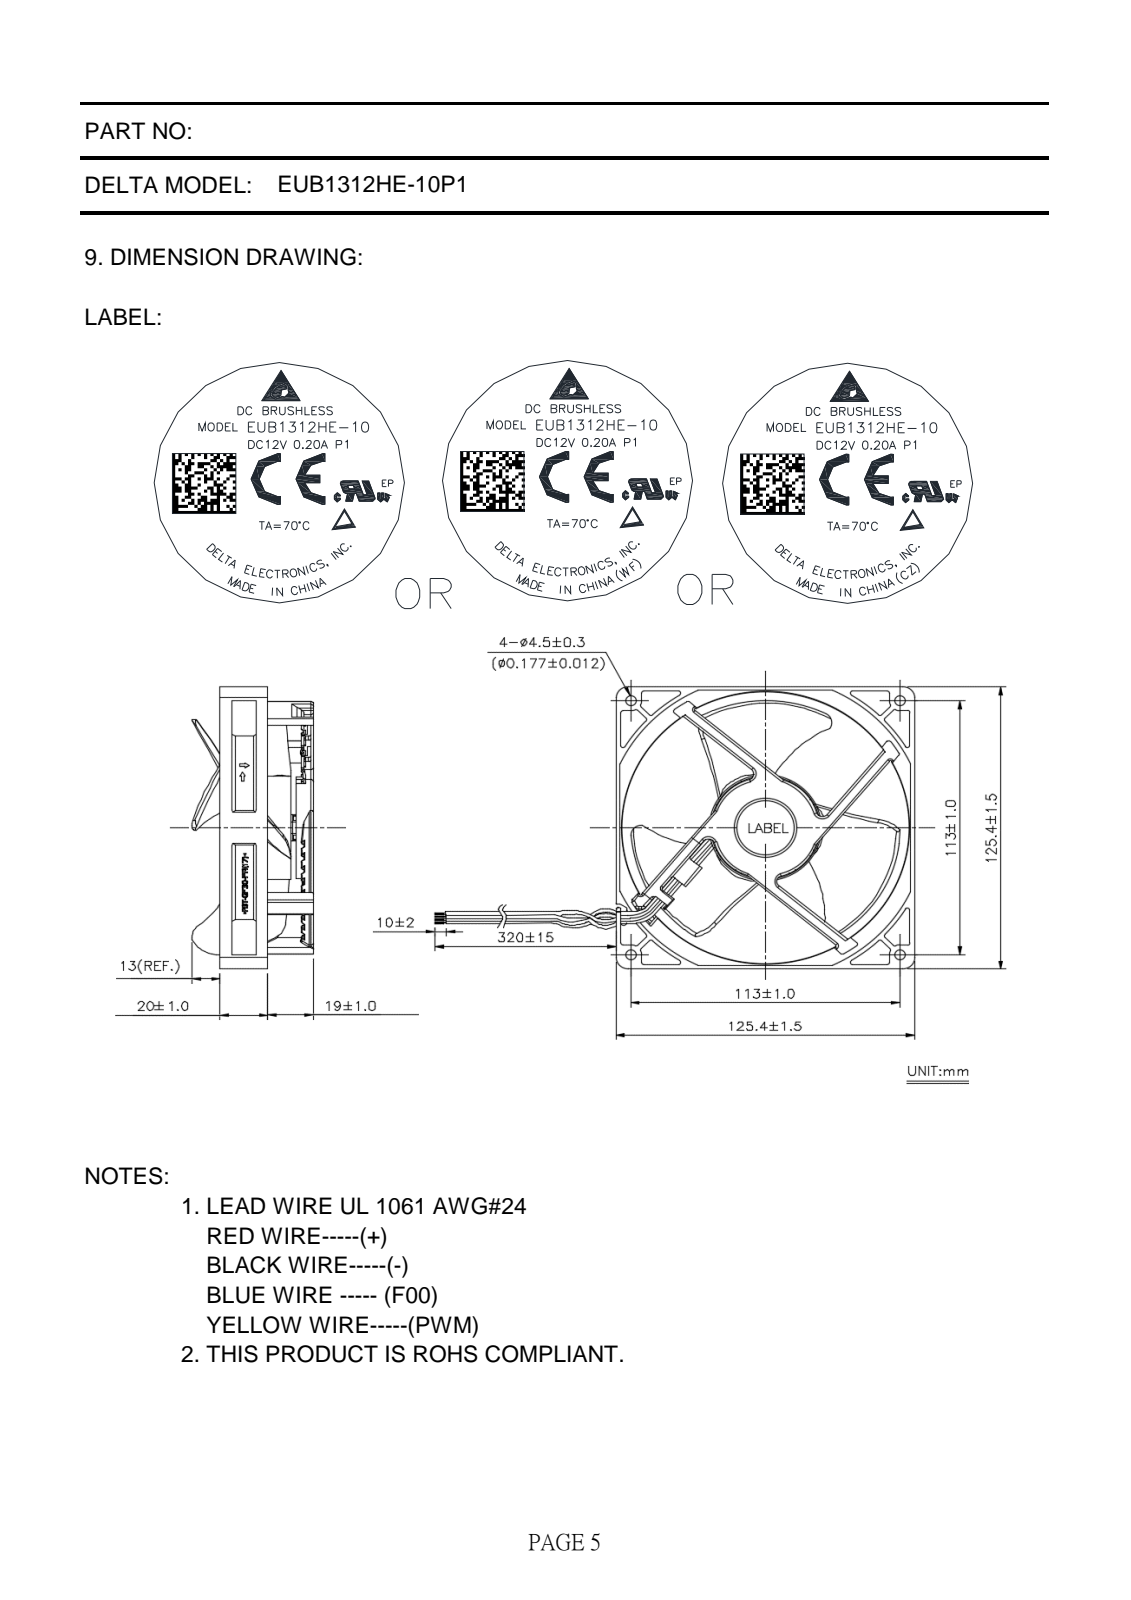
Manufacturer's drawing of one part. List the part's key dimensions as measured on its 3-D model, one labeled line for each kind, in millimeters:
Part name (STEP PRODUCT): A125-P1-FRAME; A125-P1-IMPELLER; A125-P1_ASM
STEP written by: CREO PARAMETRIC BY PTC INC, 2015080 (AUTOMOTIVE_DESIGN)
Units: millimetres
Bodies: 2 solids, 1373 faces (722 planar, 418 cylindrical, 233 other)
Overall size (bounding box): 125.4 × 125.4 × 48.62
Volume: 146 432 mm³ · Surface area: 62 329 mm²
Round holes (diameter × count): ⌀4.5 ×4, ⌀26 ×1, ⌀121 ×1
Round bosses / shafts (diameter × count): ⌀47 ×1, ⌀45 ×1
Partial cylindrical surfaces — rounded edges, fillets, slot ends (radius × count): R0.2 ×107, R1 ×86, R0.5 ×17, R2 ×4, R2.5 ×4, R4.5 ×4, R5 ×4, R0.3 ×1
Main face-to-face distances: 5, 15, 125.4, 2, 10, 3, 34.07, 18, 13, 14.78
Hole centre spacings: 79.9, 113, 159.81
